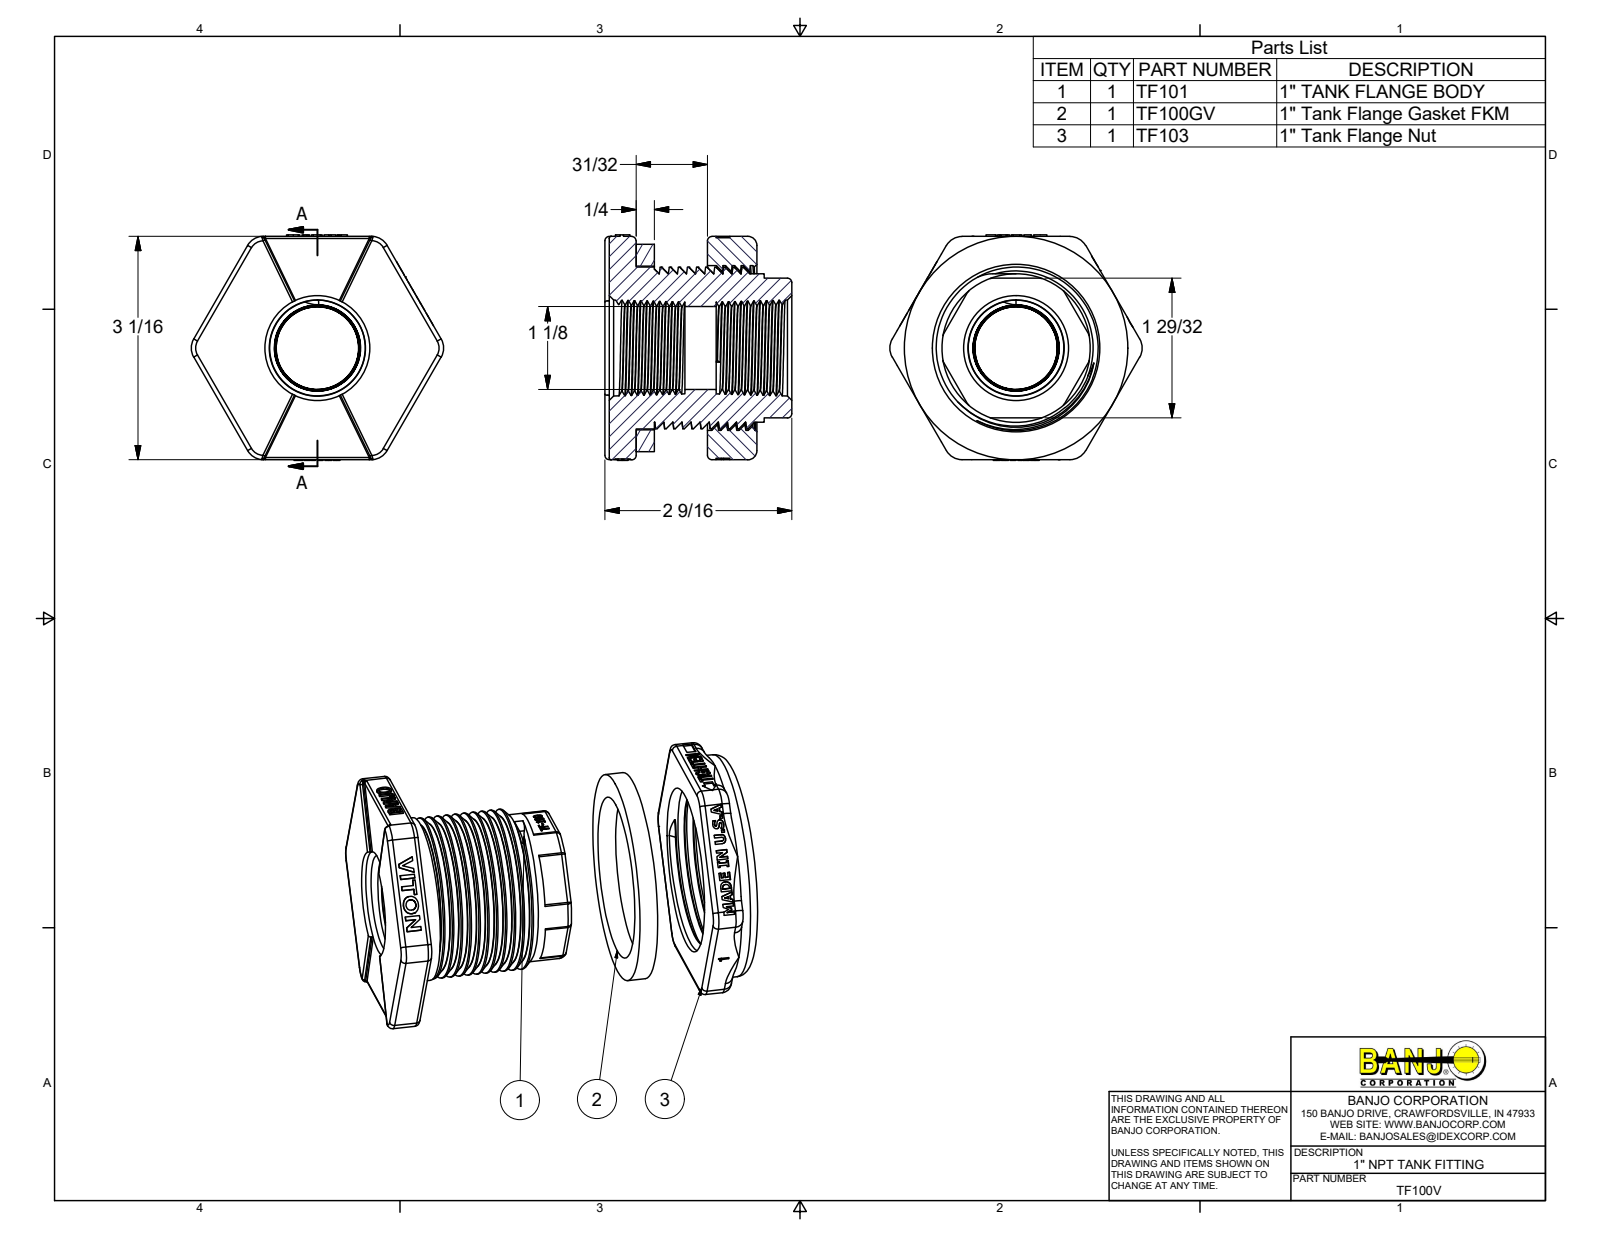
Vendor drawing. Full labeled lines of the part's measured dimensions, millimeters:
Part name (STEP PRODUCT): TF100V; TF101; TF103; TF103X (+2 more)
STEP written by: Autodesk Inventor 2017 (AUTOMOTIVE_DESIGN)
Units: millimetres
Bodies: 8 solids, 922 faces (543 planar, 99 cylindrical, 280 other)
Overall size (bounding box): 88.08 × 78.74 × 65.28
Volume: 182 494 mm³ · Surface area: 56 057 mm²
Round holes (diameter × count): ⌀28.96 ×1, ⌀53.85 ×1, ⌀56.52 ×1, ⌀57.53 ×1
Round bosses / shafts (diameter × count): ⌀77.98 ×1, ⌀72.39 ×1, ⌀57.15 ×1, ⌀56.39 ×1, ⌀51.82 ×1
Partial cylindrical surfaces — rounded edges, fillets, slot ends (radius × count): R1.52 ×28, R0.76 ×6, R1.59 ×6, R3.17 ×6, R6.35 ×6, R0.38 ×4, R10 ×1, R12.7 ×1
Main face-to-face distances: 10.92, 35.81, 24.89, 18.54, 6.35, 17.27, 35.82, 77.98, 53.09, 42.17
